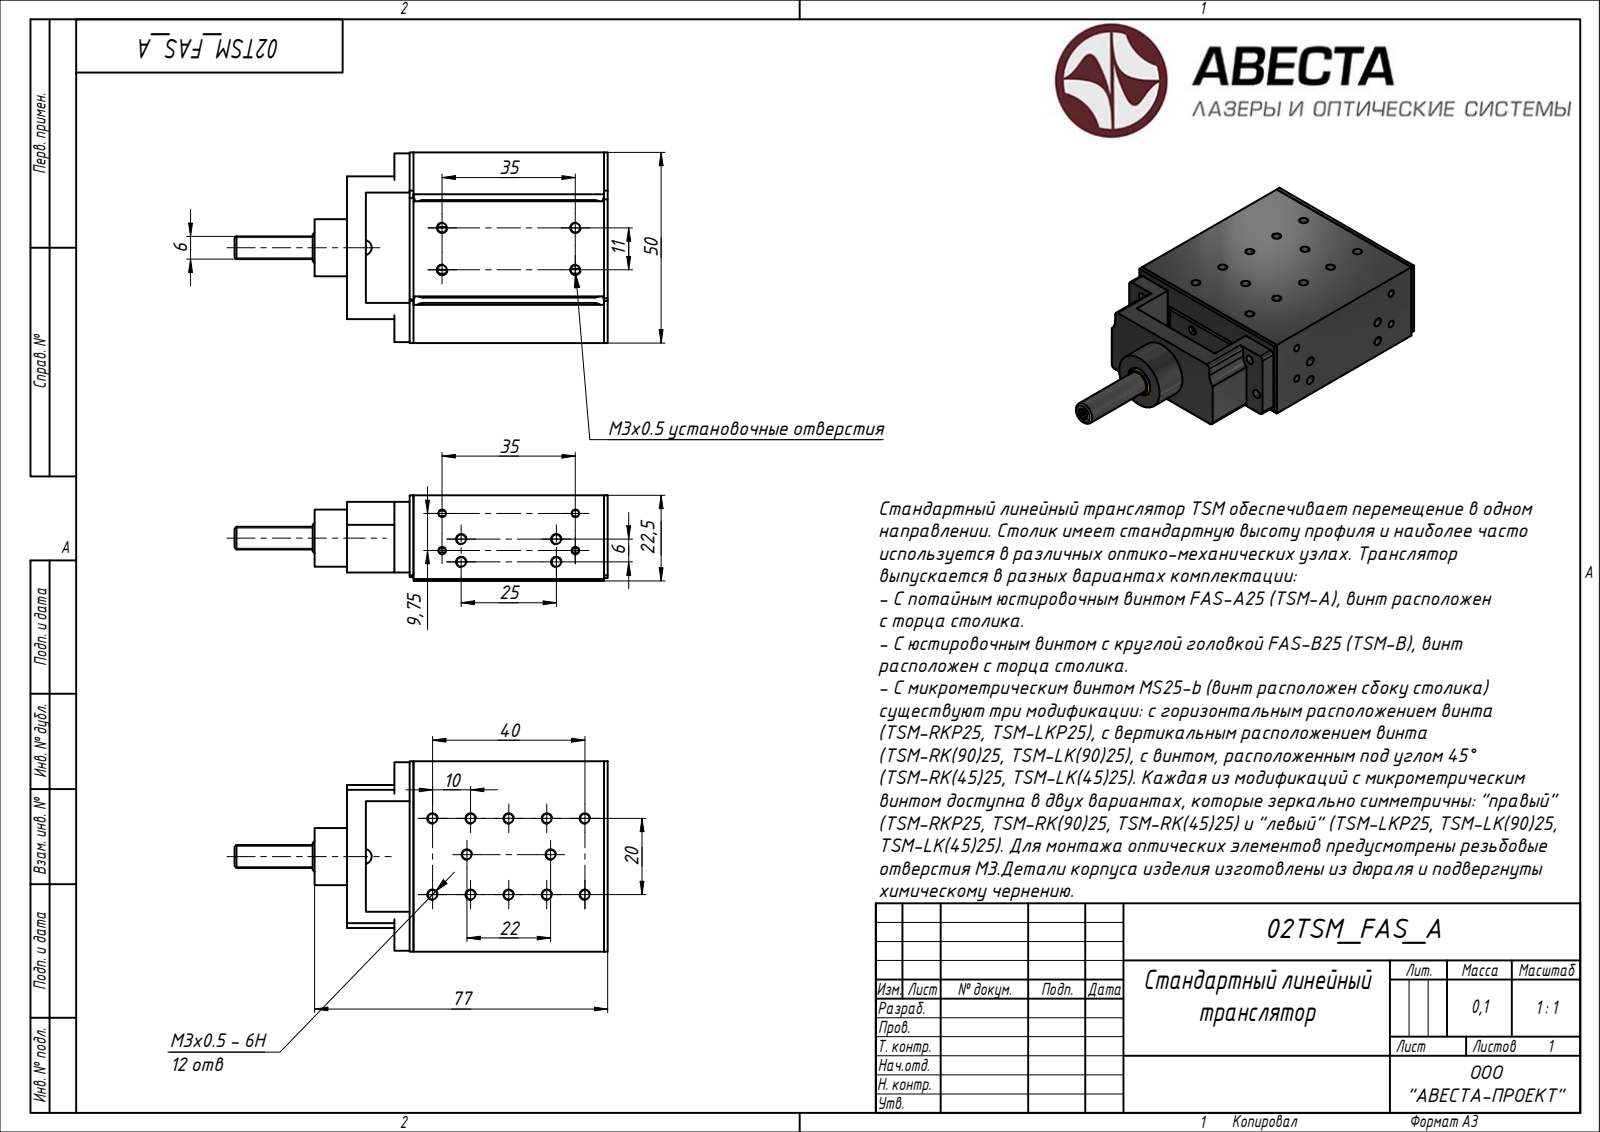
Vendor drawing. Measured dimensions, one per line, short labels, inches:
written by: ST-DEVELOPER v15 (AUTOMOTIVE_DESIGN)
unit: in
bodies: 10 solids, 481 faces (0 planar, 0 cylindrical, 481 other)
size: 3.543 × 1.969 × 0.886
